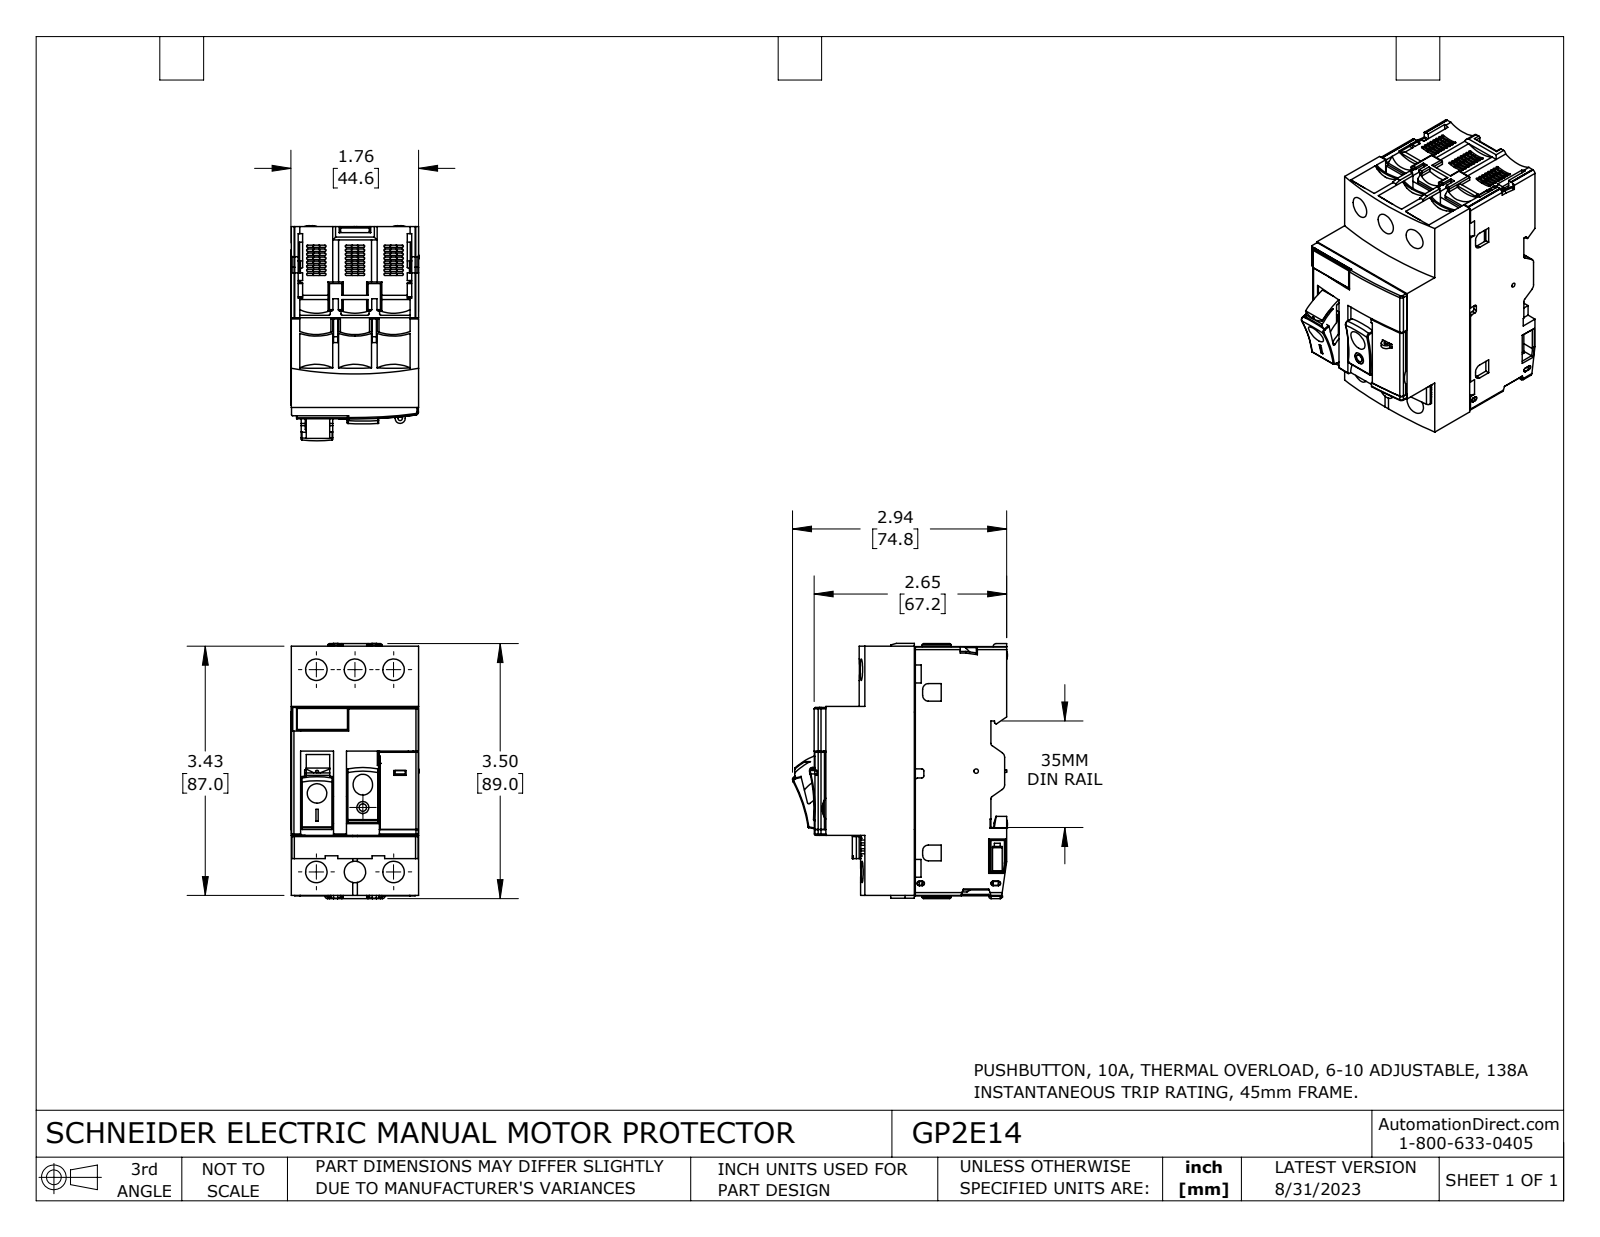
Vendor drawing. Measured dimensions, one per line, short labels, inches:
name: GP2E14
written by: SolidWorks 2021 (CONFIG_CONTROL_DESIGN)
unit: in
bodies: 15 solids, 2269 faces (1521 planar, 657 cylindrical, 91 other)
size: 3.508 × 2.957 × 1.764
volume: 11.58 in³; area: 98.93 in²
holes: 6× ⌀0.295, 5× ⌀0.197, 2× ⌀0.059, 1× ⌀0.157, 1× ⌀0.165, 1× ⌀0.315, 1× ⌀0.327, 1× ⌀0.335, 1× ⌀0.343
bosses: 2× ⌀0.244, 2× ⌀0.118, 1× ⌀0.382, 1× ⌀0.102, 1× ⌀0.047
rounds: 104× R0.016, 47× R0.02, 16× R0.039, 12× R0.01, 12× R0.012, 12× R0.031, 8× R0.059, 6× R0.004
face distances: 1.752, 0.531, 0.115, 1.233, 1.756, 0.059, 1.637, 0.581, 1.053, 1.171
hole spacings: 0.531, 2.83, 2.779, 0.346, 0.402, 0.546, 0.671, 0.726
